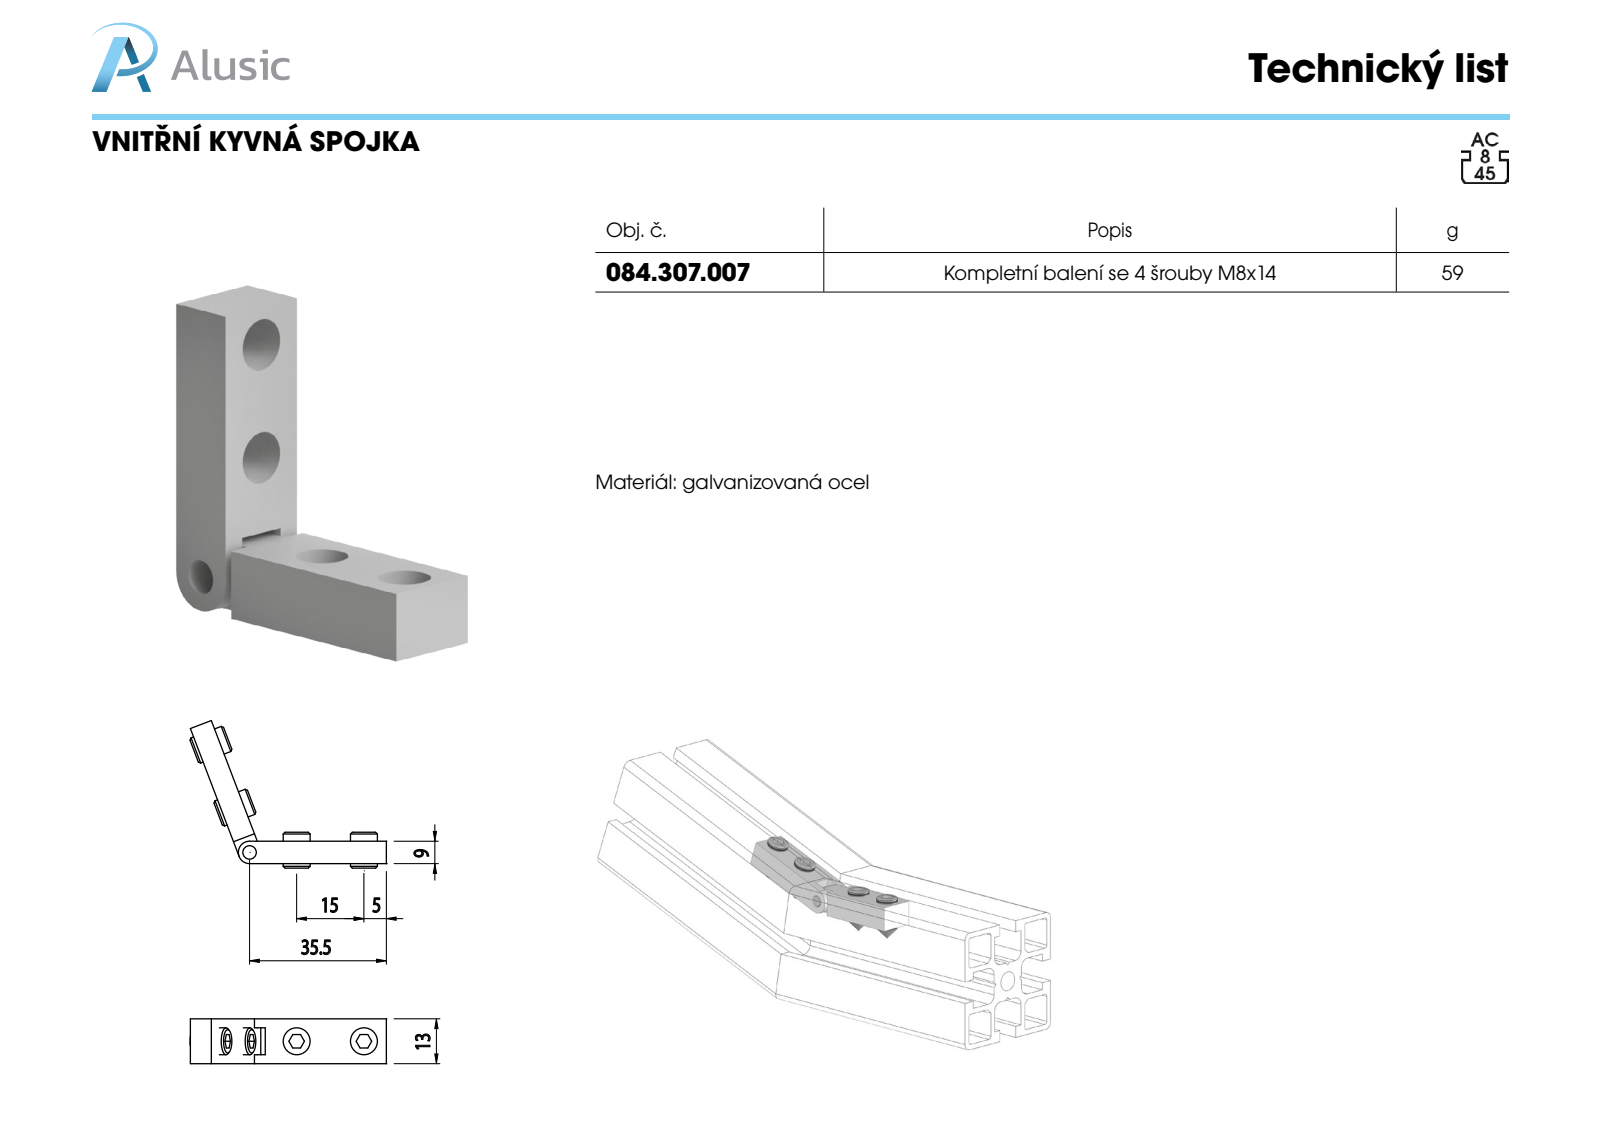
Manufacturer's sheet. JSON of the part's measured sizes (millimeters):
{"part_name": "084.307.007A; 084.307.007B; 084.307.007", "step_written_by": "SolidWorks 2011 (CONFIG_CONTROL_DESIGN)", "units": "millimeters", "bodies": {"solids": 2, "faces": 37, "planar": 17, "cylindrical": 20, "other": 0}, "overall_size": [68.13, 26.86, 13], "volume_mm3": 6563, "surface_area_mm2": 4373, "round_holes": [[6.8, 4], [4.5, 1]], "round_bosses_or_shafts": [[9, 1]], "face_to_face_distances": [13, 9, 9.01, 3, 10, 7, 30], "hole_center_spacings": [15]}
